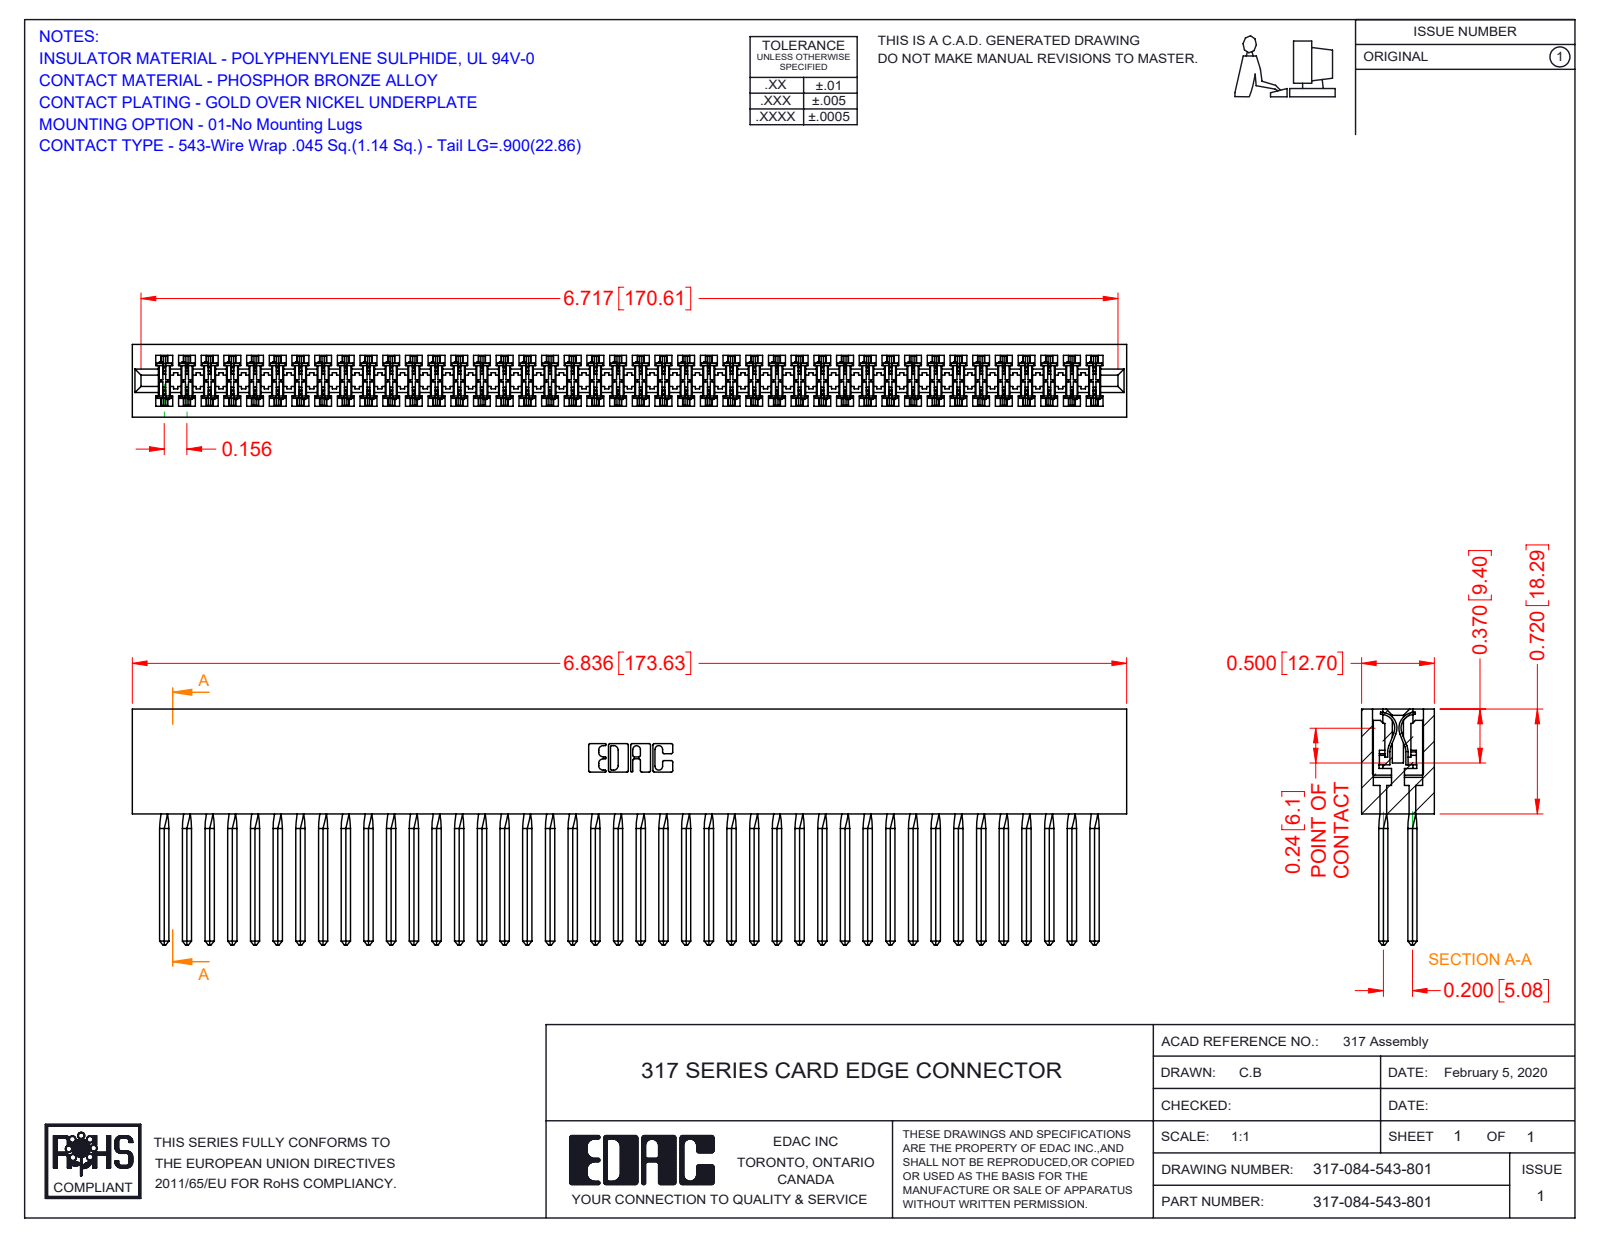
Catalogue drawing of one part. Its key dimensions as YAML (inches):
part_name: "317-084-543-801; 317-290-001_543; 317 Part_Lugless"
step_written_by: "SolidWorks 2016 (CONFIG_CONTROL_DESIGN)"
units: inches
bodies: {solids: 85, faces: 7566, planar: 6182, cylindrical: 1048, other: 336}
overall_size: [6.836, 1.62, 0.5]
volume: 1.913
surface_area: 74.15
partial_cylinders:
  - {radius: 0.015, count: 168}
  - {radius: 0.01, count: 22}
  - {radius: 0.007, count: 6}
  - {radius: 0.031, count: 6}
  - {radius: 0.026, count: 3}
  - {radius: 0.095, count: 2}
  - {radius: 0.1, count: 2}
  - {radius: 0.11, count: 2}
face_to_face_distances: [0.075, 0.5, 0.425, 0.35, 0.195, 0.11, 0.094, 0.2, 0.115, 0.131]
